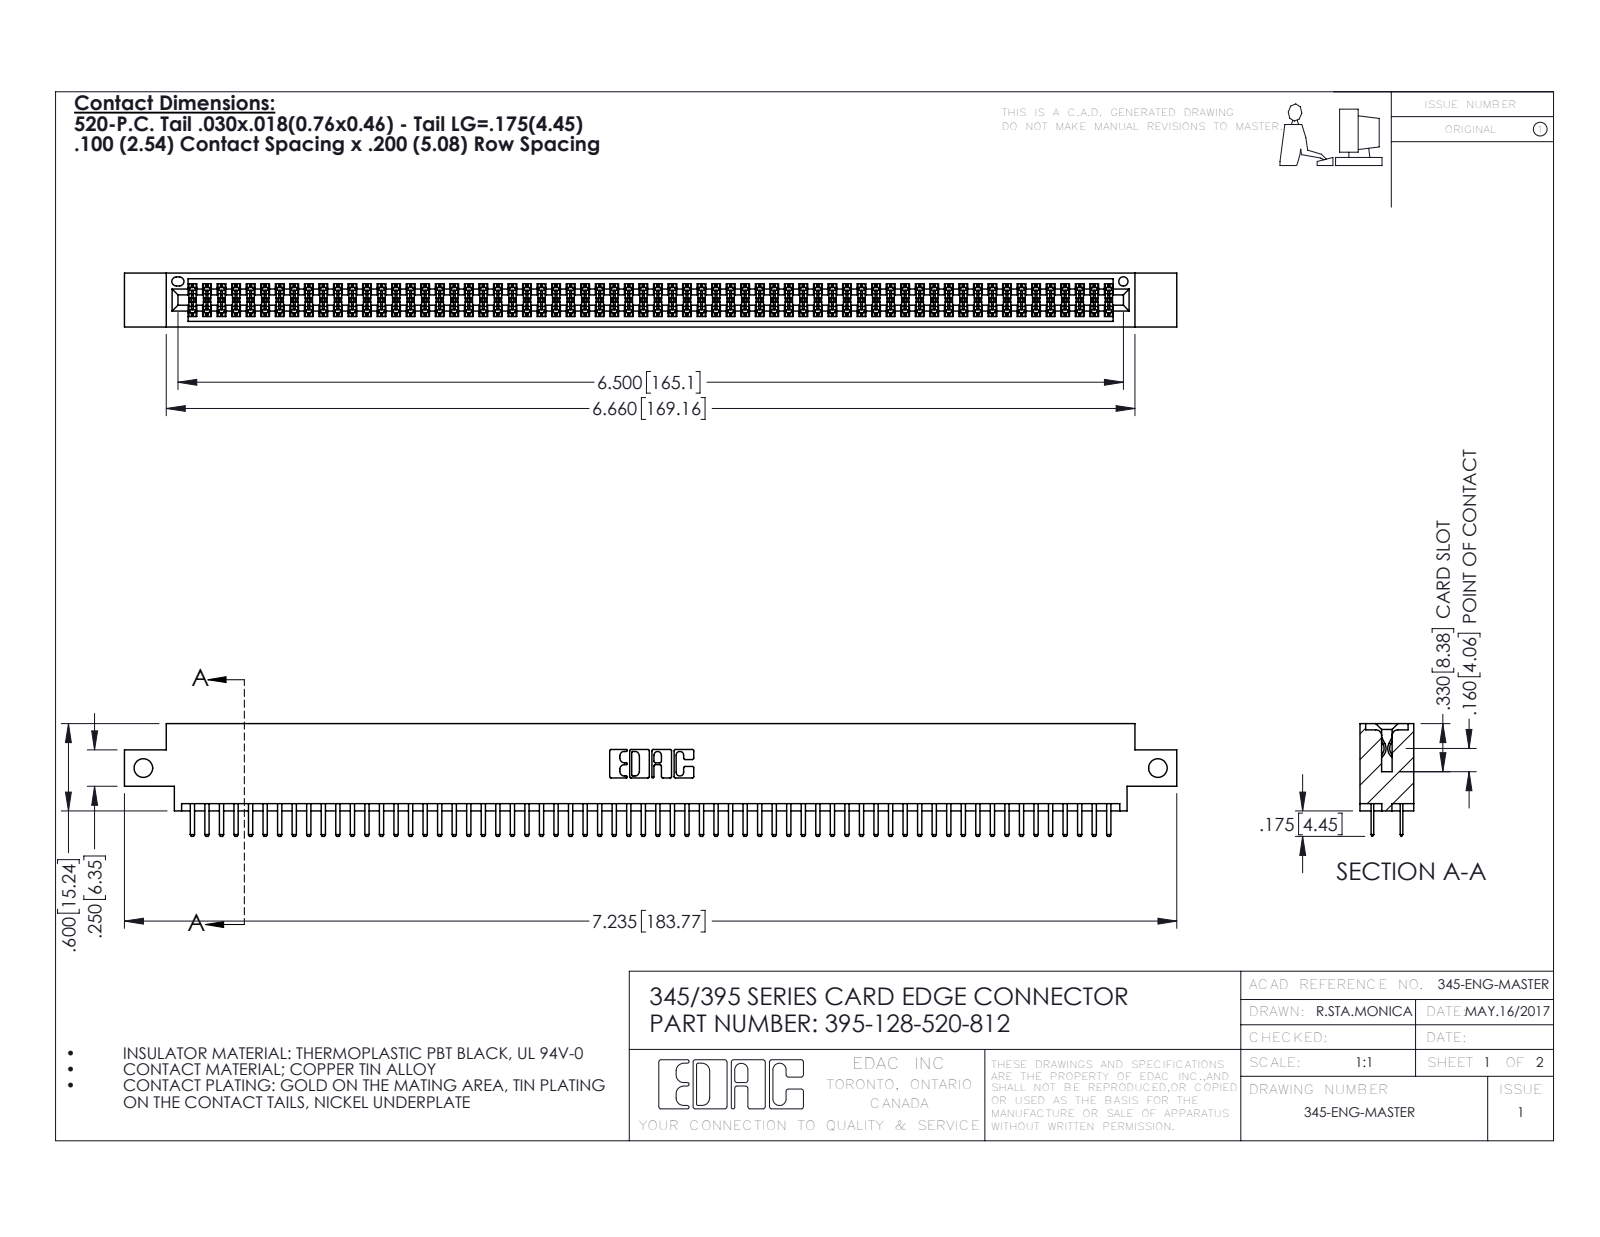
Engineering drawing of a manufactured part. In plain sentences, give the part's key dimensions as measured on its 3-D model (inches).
The part is named "345-292-001_345-293-120; 345 Part_0.170 Offset - Side Mount; 395-128-520-812". Its 3-D file was written by "SolidWorks 2016 (CONFIG_CONTROL_DESIGN)". It is 129 solids with 7042 faces: 4564 planar, 2478 cylindrical and 0 other. Overall it measures 7.235 by 0.775 by 0.37 inches. Its volume is 1.086 cubic inches and its surface area 41.27 square inches. Round holes: 2 of diameter 0.128, 1 of diameter 0.064. Partial cylindrical surfaces (rounded edges, fillets, slot ends): 192 of radius 0.006, 132 of radius 0.01, 22 of radius 0.01, 6 of radius 0.007, 6 of radius 0.031, 3 of radius 0.026, 2 of radius 0.014, 2 of radius 0.019. The main face-to-face distances are 0.298, 0.072, 0.2, 0.37, 0.098, 0.272, 0.025, 0.225, 0.022, 0.072. The hole center spacings are 6.975.
